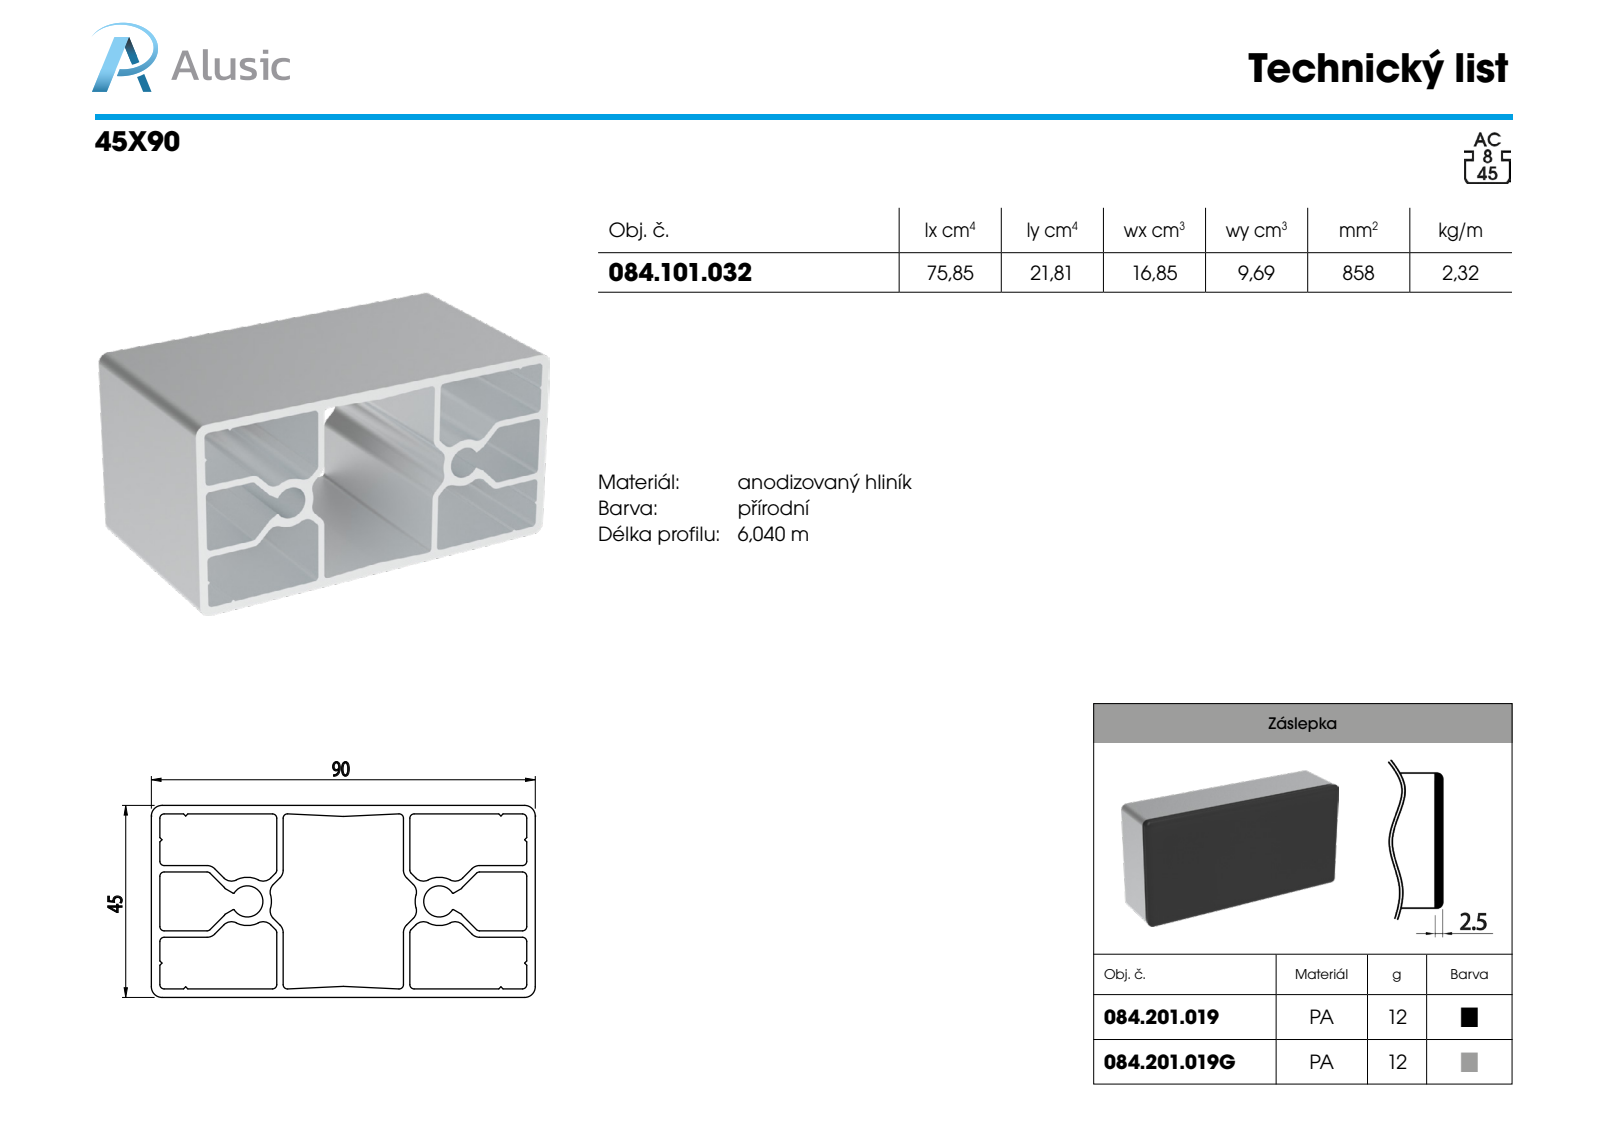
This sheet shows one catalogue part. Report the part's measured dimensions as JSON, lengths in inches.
{"part_name": "084.101.032", "step_written_by": "SolidWorks 2018 (AUTOMOTIVE_DESIGN)", "units": "inches", "bodies": {"solids": 1, "faces": 162, "planar": 80, "cylindrical": 82, "other": 0}, "overall_size": [3.937, 3.543, 1.772], "volume_in3": 5.253, "surface_area_in2": 138.6, "round_holes": [[0.287, 2]], "partial_cylinders_radius": [[0.039, 32], [0.098, 24], [0.008, 4], [0.222, 2]], "face_to_face_distances": [0.079, 0.059, 1.693, 1.217, 1.157, 1.772, 1.138, 1.079, 1.614, 2.327], "hole_center_spacings": [1.772]}
